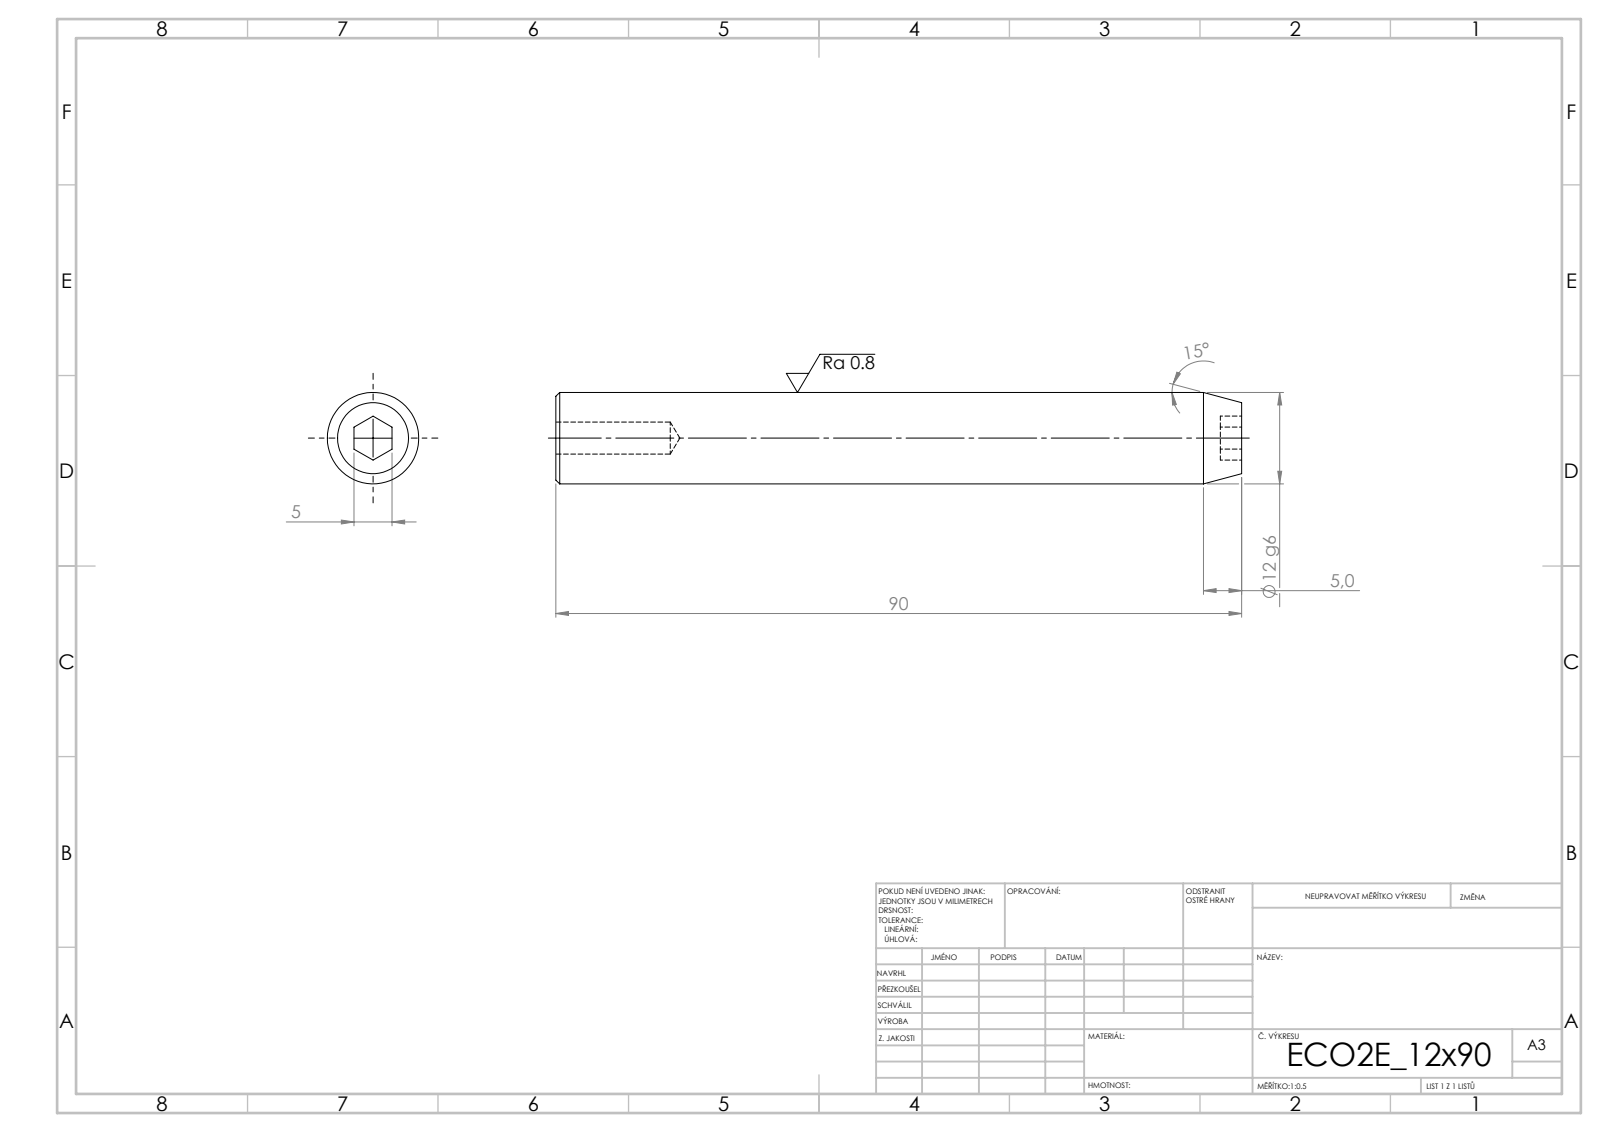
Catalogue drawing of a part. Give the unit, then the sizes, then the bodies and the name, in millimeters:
Units: millimetres
Overall size (bounding box): 90 × 12 × 12
Round holes (diameter × count): ⌀4.2 ×1
Round bosses / shafts (diameter × count): ⌀12 ×1
Main face-to-face distances: 90, 5, 2.8, 87.2
Volume: 9 783 mm³ · Surface area: 3 796 mm²
Bodies: 1 solid, 19 faces (9 planar, 4 cylindrical, 6 other)
STEP written by: SolidWorks 2019 (CONFIG_CONTROL_DESIGN)
